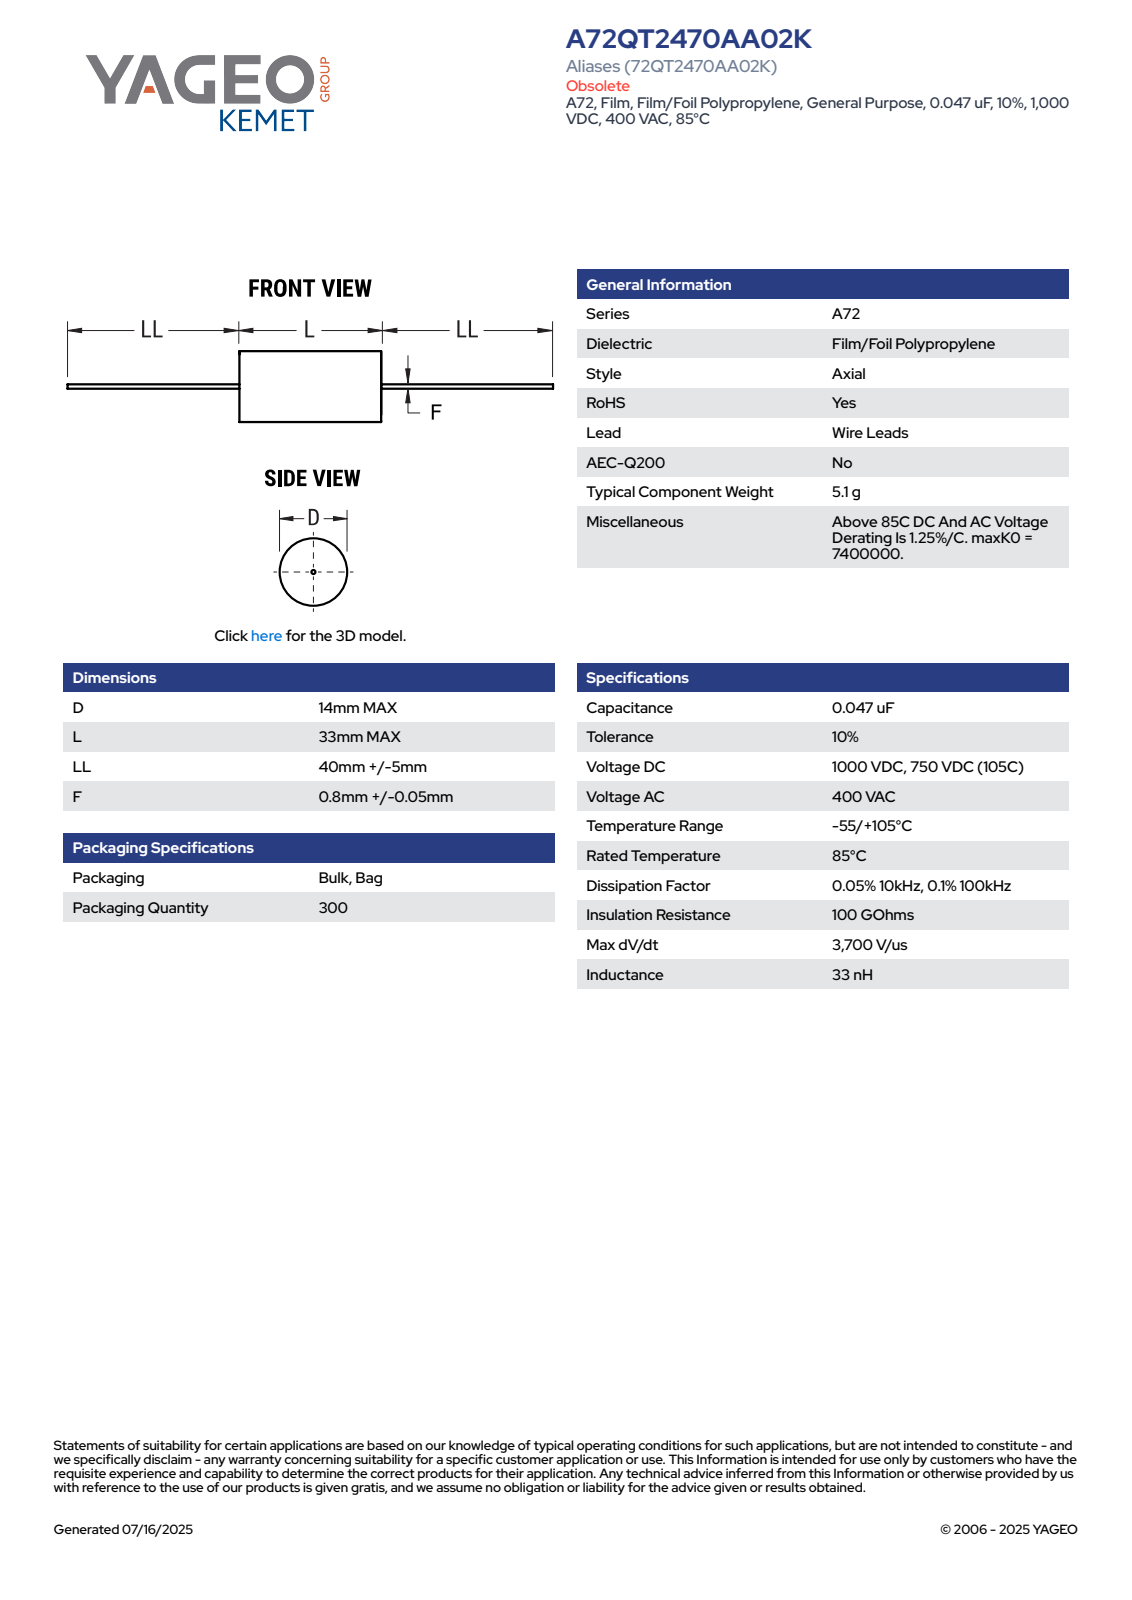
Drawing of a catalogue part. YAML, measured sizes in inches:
part_name: "CFA_ACWF_14X33_D14L33LL45F0.85"
step_written_by: "SolidWorks 2014 (AUTOMOTIVE_DESIGN)"
units: inches
bodies: {solids: 1, faces: 72, planar: 26, cylindrical: 15, other: 31}
overall_size: [4.843, 0.552, 0.551]
volume: 0.313
surface_area: 3.1
round_bosses_or_shafts:
  - {diameter: 0.551, count: 1}
  - {diameter: 0.033, count: 1}
partial_cylinders:
  - {radius: 0.276, count: 1}
face_to_face_distances: [1.299, 1.772, 3.071, 4.843]
